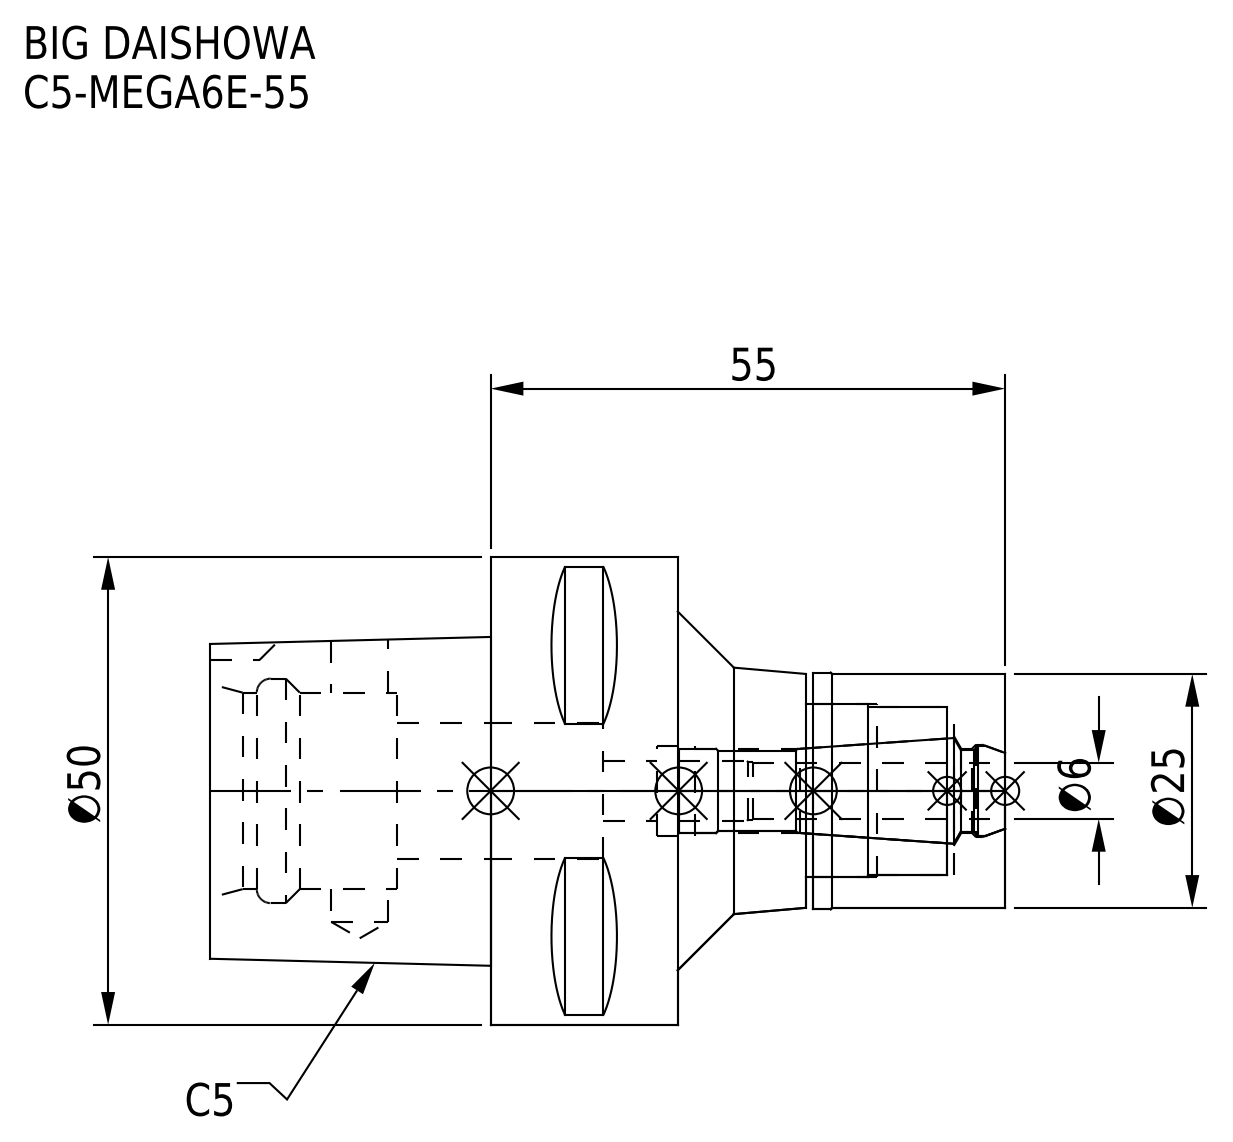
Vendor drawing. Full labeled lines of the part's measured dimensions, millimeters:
Part name (STEP PRODUCT): C5-MEGA6E-55; C5-MEGA6E-55_1.stp; C5-MEGA6E-55-060_ASM.stp; DXF_TEMP_ASSY_ASM_4_ASM.stp (+3 more)
STEP written by: SolidWorks 2019 (CONFIG_CONTROL_DESIGN)
Units: millimetres
Bodies: 2 solids, 97 faces (36 planar, 37 cylindrical, 24 other)
Overall size (bounding box): 85 × 50 × 50
Volume: 70 736 mm³ · Surface area: 19 138 mm²
Round holes (diameter × count): ⌀6.1 ×1, ⌀6.4 ×1, ⌀9 ×1, ⌀9.6 ×1, ⌀9.9 ×1, ⌀14.5 ×1, ⌀18 ×1, ⌀18.5 ×1, ⌀21 ×1, ⌀24 ×1
Round bosses / shafts (diameter × count): ⌀50 ×1, ⌀25.3 ×1, ⌀25 ×1
Partial cylindrical surfaces — rounded edges, fillets, slot ends (radius × count): R4 ×1
Main face-to-face distances: 20, 30, 35, 55, 85, 50, 13.7, 21.3, 20.5, 14.5
